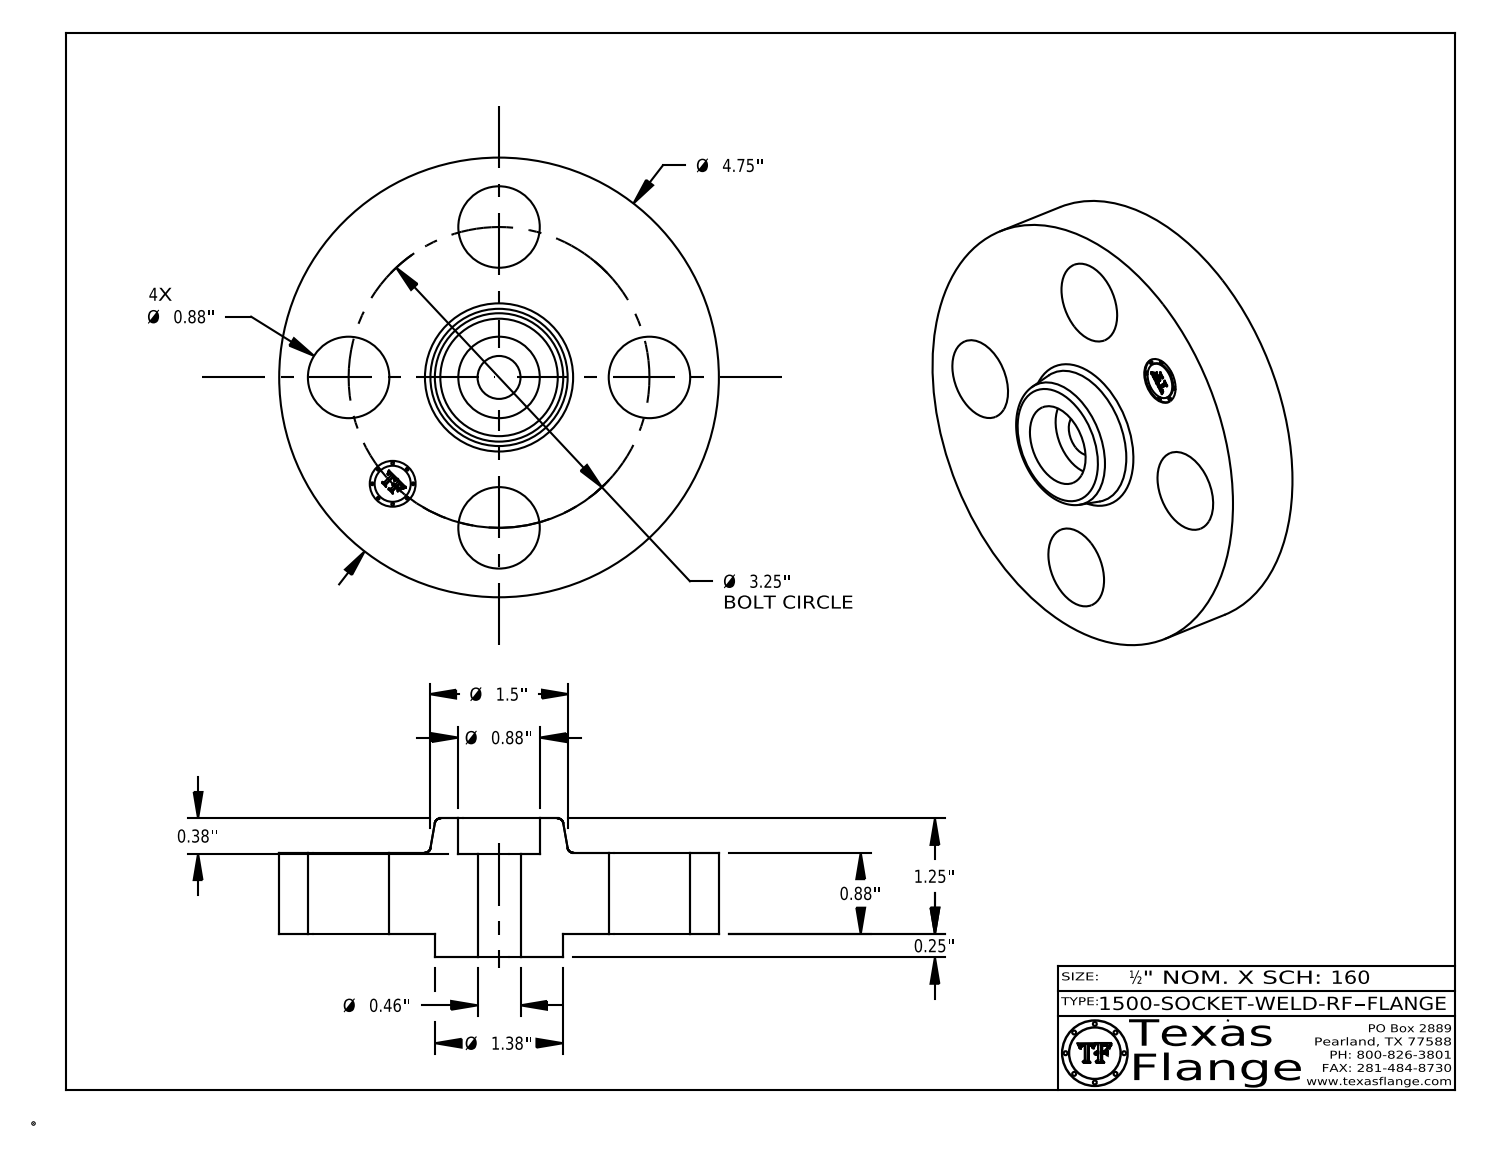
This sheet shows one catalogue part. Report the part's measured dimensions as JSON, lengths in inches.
{"part_name": "1500-SOCKET-WELD-RF", "step_written_by": "CATIA V5 STEP AP214 (AUTOMOTIVE_DESIGN)", "units": "inches", "bodies": {"solids": 1, "faces": 412, "planar": 370, "cylindrical": 36, "other": 6}, "overall_size": [4.75, 4.75, 1.5], "volume_in3": 14, "surface_area_in2": 58.21, "round_holes": [[0.88, 5], [0.464, 1], [0.495, 1]], "round_bosses_or_shafts": [[0.03, 8], [4.75, 1], [1.38, 1], [0.39, 1]], "face_to_face_distances": [0.88, 0.25, 1.13, 1.5, 1.25, 0.37, 1.12, 0.87, 0.38, 1.115], "hole_center_spacings": [1.625, 2.298, 1.244, 3.003, 3.25]}
